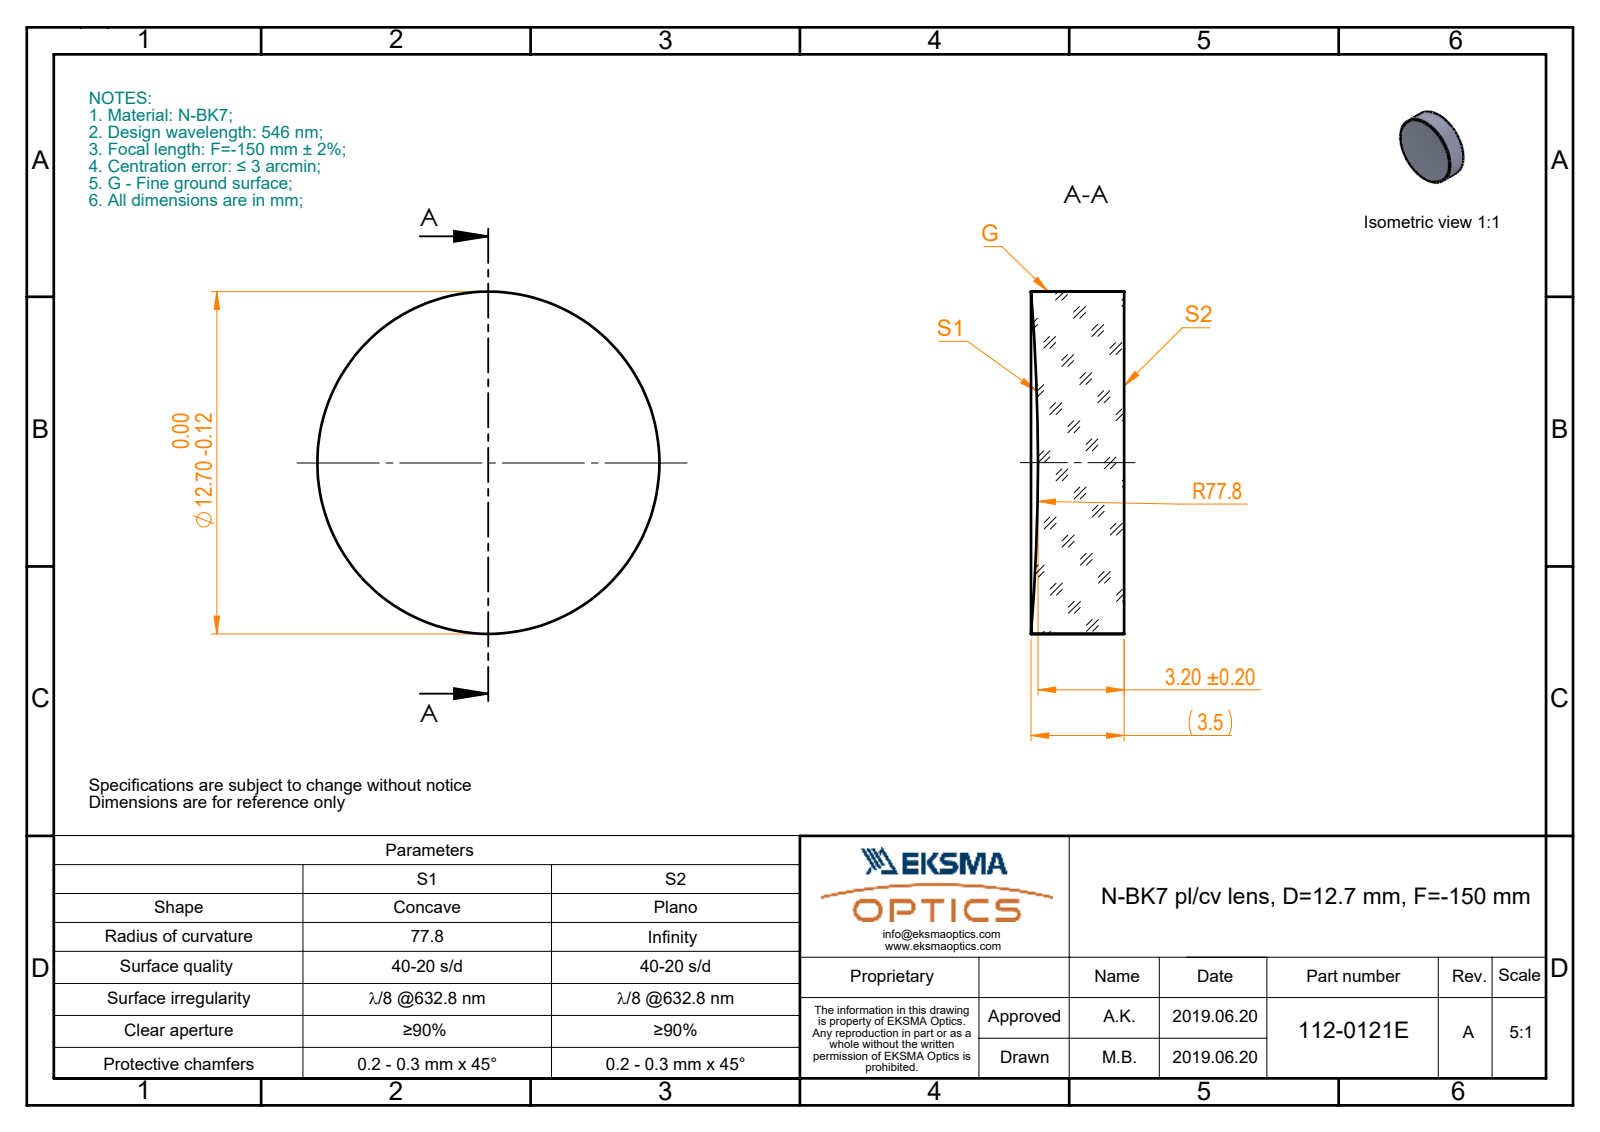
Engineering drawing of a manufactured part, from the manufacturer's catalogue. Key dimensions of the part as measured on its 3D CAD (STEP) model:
Part name (STEP PRODUCT): 112-0121E BK7 pl-cv 12.7 F-150
STEP written by: SolidWorks 2017 (CONFIG_CONTROL_DESIGN)
Units: millimetres
Bodies: 1 solid, 5 faces (1 planar, 2 cylindrical, 2 other)
Overall size (bounding box): 12.7 × 12.7 × 3.46
Volume: 422 mm³ · Surface area: 392 mm²
Round bosses / shafts (diameter × count): ⌀12.7 ×1
